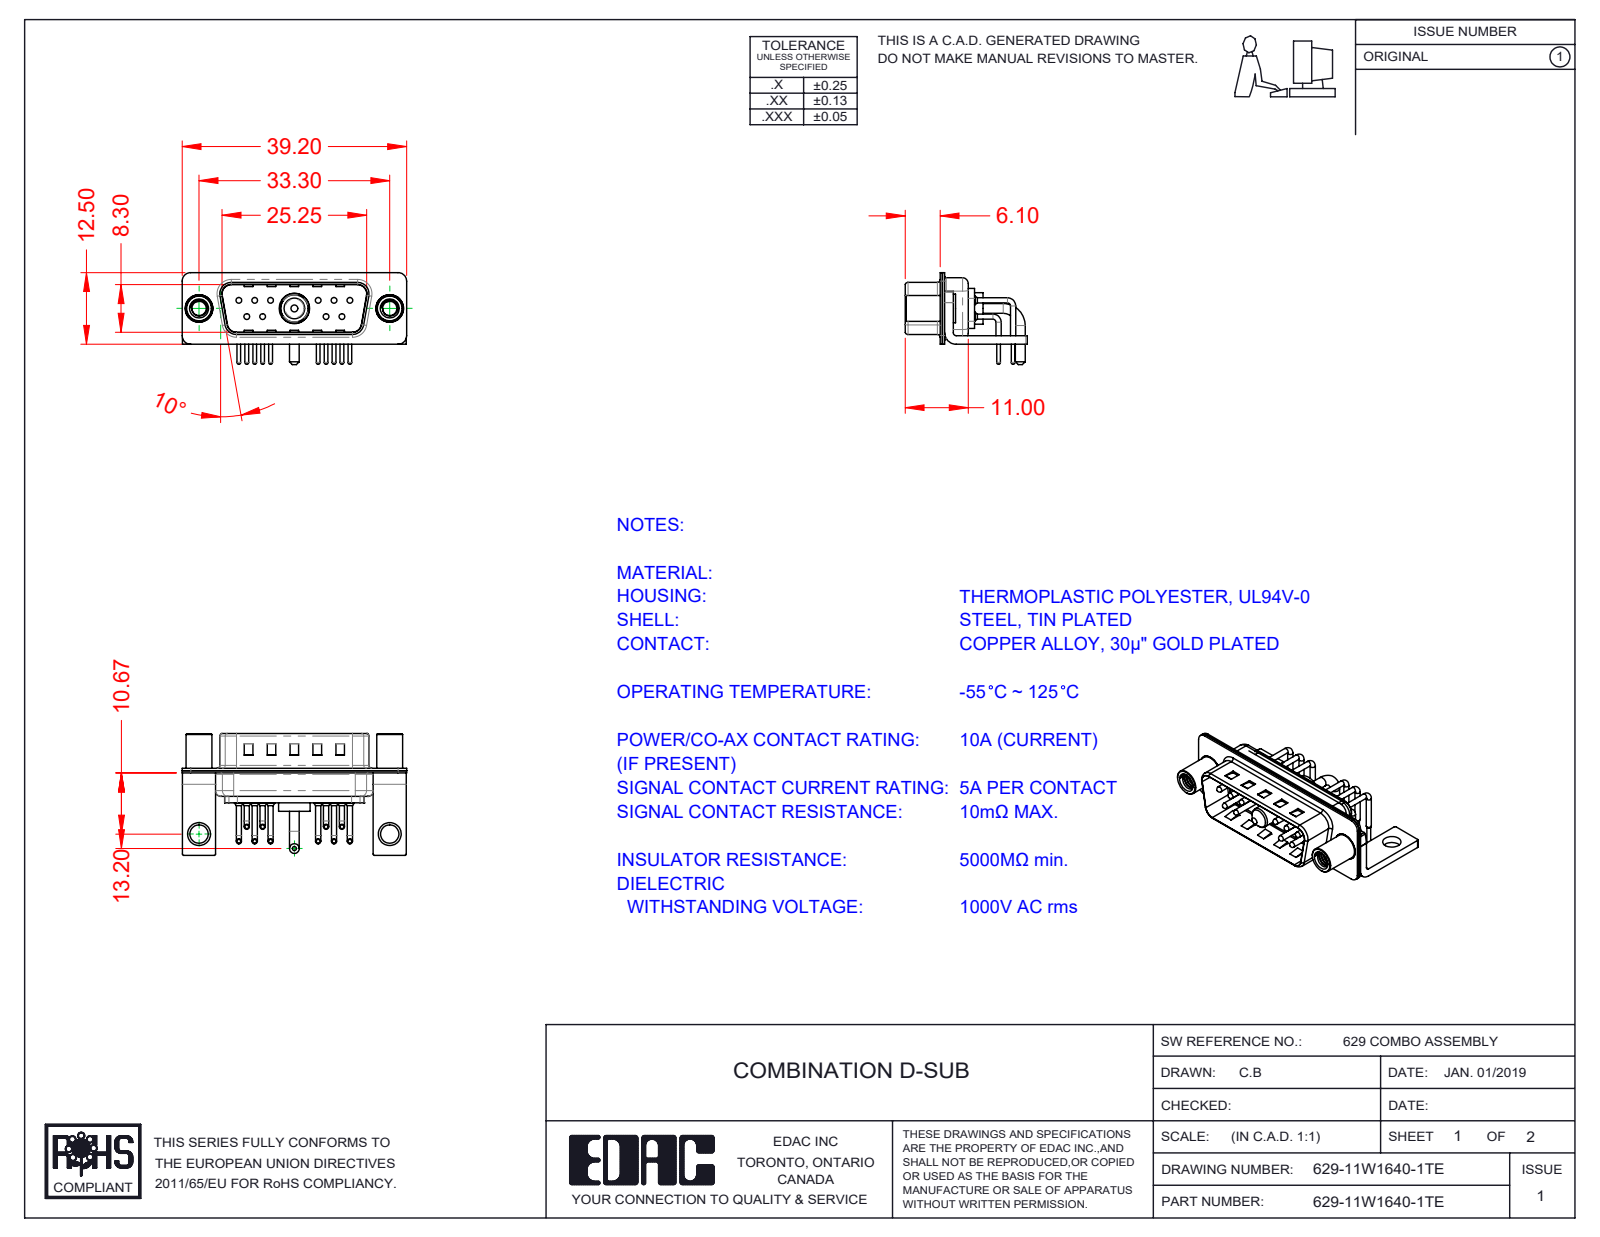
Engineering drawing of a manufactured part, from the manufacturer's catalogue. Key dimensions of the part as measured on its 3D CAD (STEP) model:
Part name (STEP PRODUCT): 629-11W1640-1TE; 629Combo Contact Row 1; 629Combo Contact Row 2; 629Combo Stabilizer Bracket (+5 more)
STEP written by: SolidWorks 2020 (CONFIG_CONTROL_DESIGN)
Units: millimetres
Bodies: 19 solids, 1594 faces (820 planar, 590 cylindrical, 184 other)
Overall size (bounding box): 39.2 × 21.3 × 16.05
Volume: 2 389 mm³ · Surface area: 6 107 mm²
Round holes (diameter × count): ⌀0.75 ×10, ⌀1.6 ×10, ⌀2 ×10, ⌀2.5 ×2, ⌀3.2 ×2, ⌀4 ×2, ⌀4.8 ×2, ⌀4.85 ×1, ⌀5.3 ×1
Round bosses / shafts (diameter × count): ⌀0.9 ×20, ⌀1.5 ×10, ⌀1 ×10, ⌀0.65 ×10, ⌀5 ×2, ⌀4.9 ×2, ⌀4.5 ×2, ⌀1.7 ×2
Partial cylindrical surfaces — rounded edges, fillets, slot ends (radius × count): R0.25 ×16, R1.5 ×16, R2 ×13, R1.01 ×10, R0.5 ×9, R1.6 ×8, R1 ×7, R0.6 ×4
Main face-to-face distances: 0.4, 0.8, 1.5, 9.5, 9.1, 8.7, 9.9, 0.6, 1.9, 5.2
Hole centre spacings: 3.16, 2.77, 13.85, 11.08, 16.62, 5.03, 5.04, 5.54
